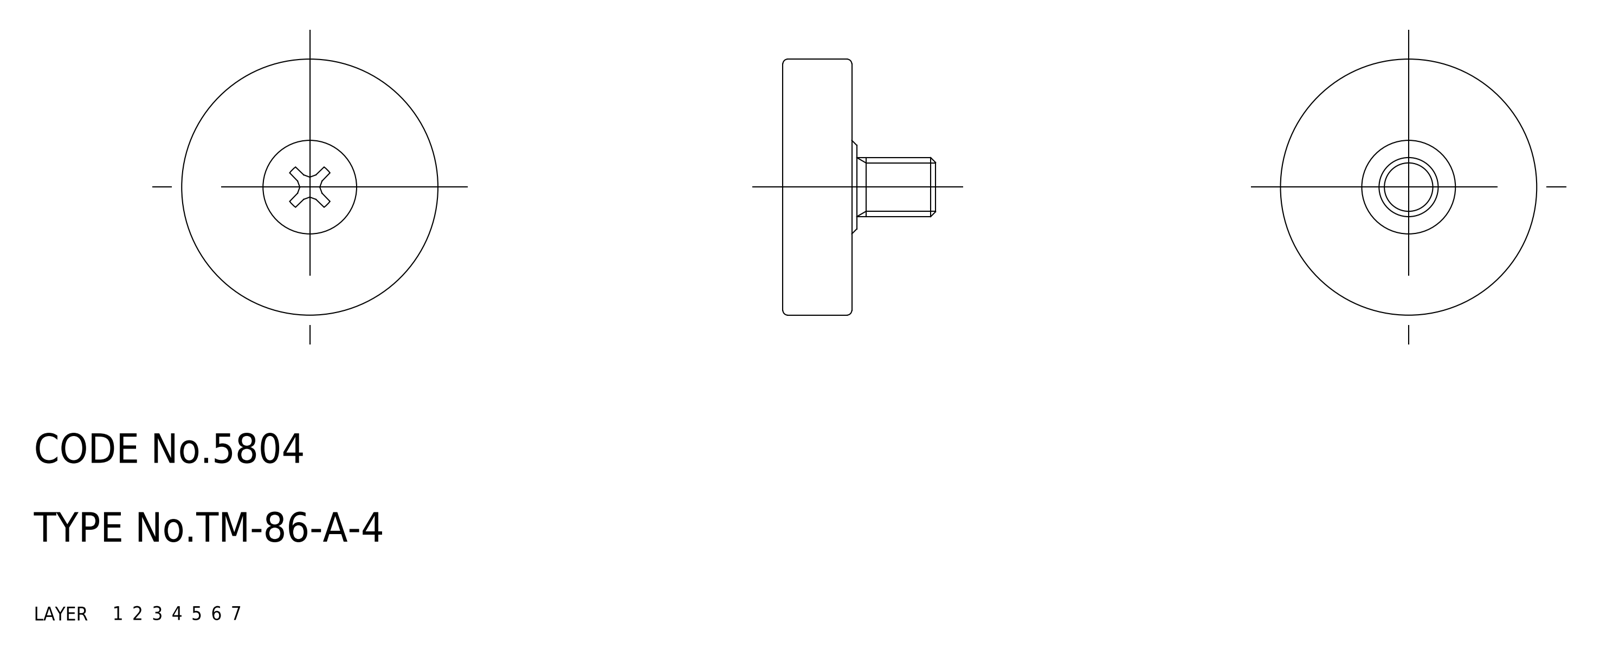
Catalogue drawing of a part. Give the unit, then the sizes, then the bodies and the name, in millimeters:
Units: millimetres
Overall size (bounding box): 26 × 26 × 15.5
Volume: 3 955 mm³ · Surface area: 2 268 mm²
Bodies: 1 solid, 49 faces (0 planar, 0 cylindrical, 49 other)
Part name (STEP PRODUCT): roller
STEP written by: CADfix (AUTOMOTIVE_DESIGN)
